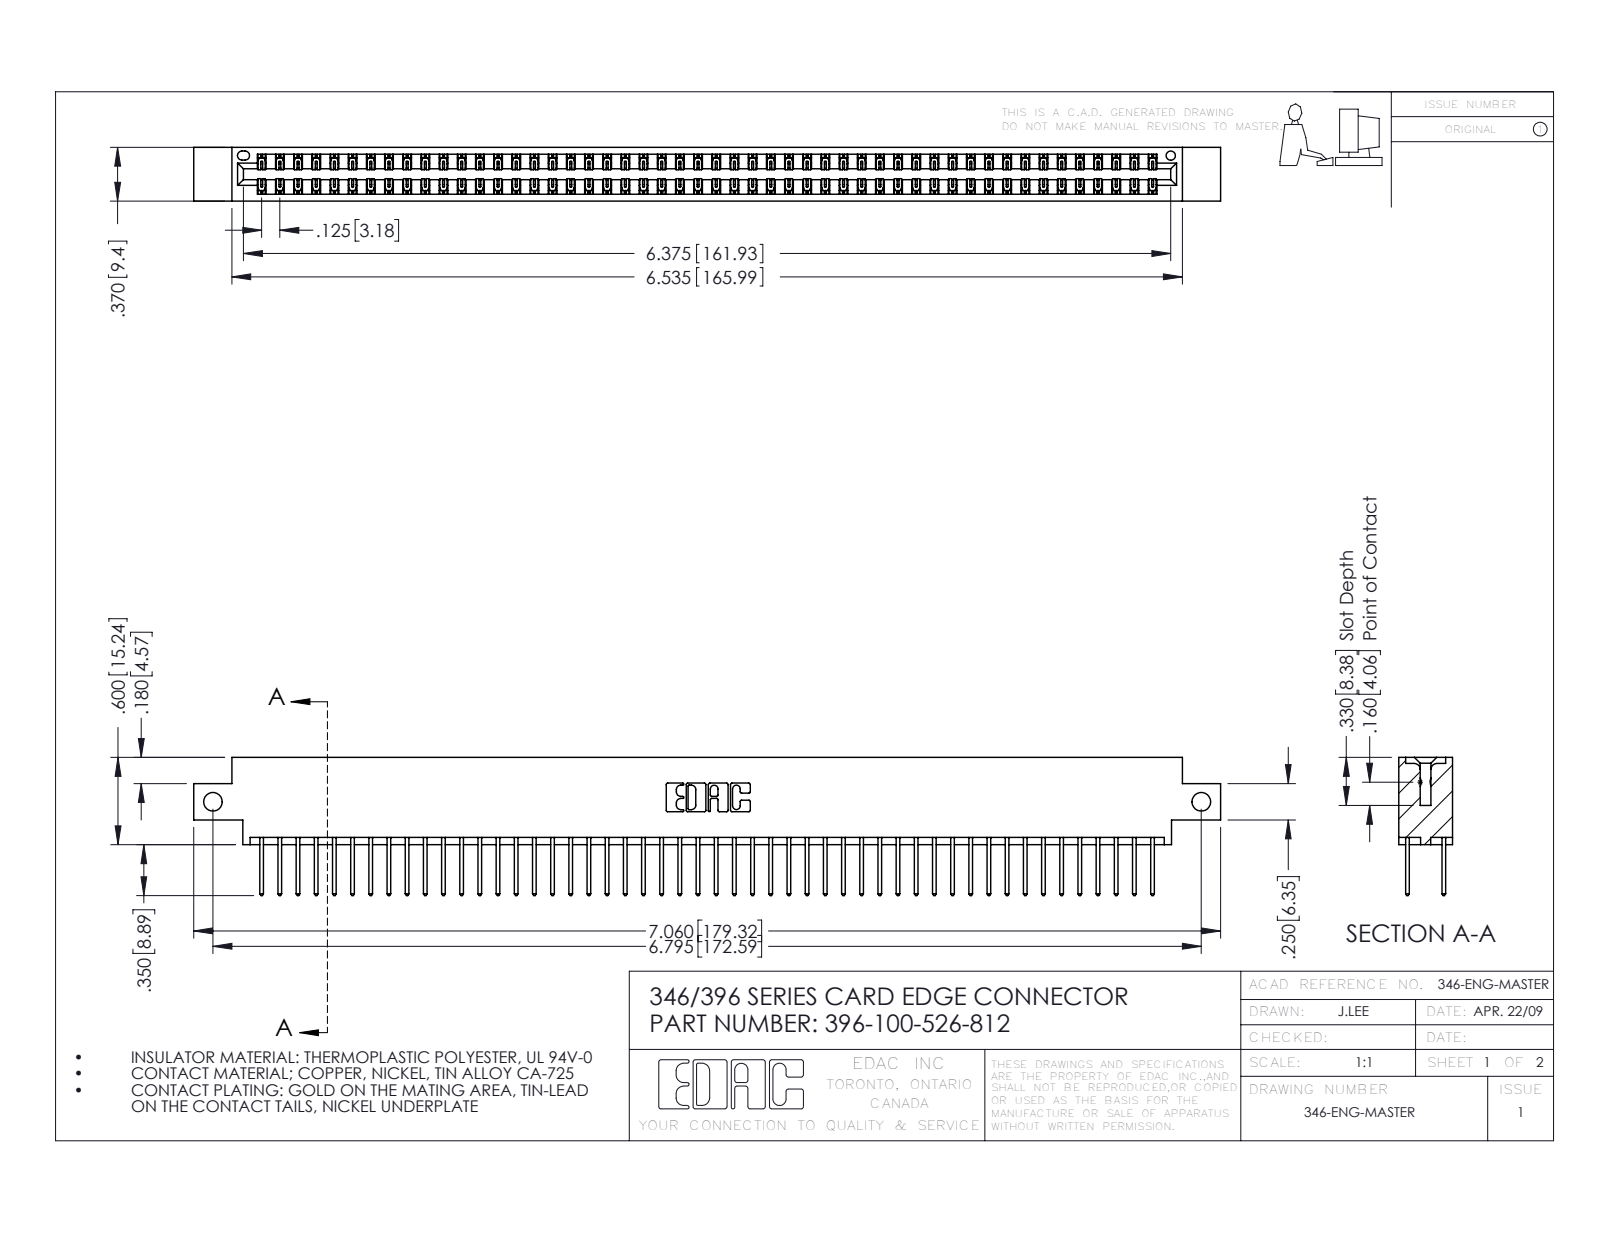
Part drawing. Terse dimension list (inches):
name: 396-100-526-812; 346 Part_0.170 Offset - Side Mount; 345-292-001_345-293-126
written by: SolidWorks 2016 (CONFIG_CONTROL_DESIGN)
unit: in
bodies: 101 solids, 5326 faces (3580 planar, 1746 cylindrical, 0 other)
size: 7.06 × 0.95 × 0.37
volume: 1.066 in³; area: 38.62 in²
holes: 2× ⌀0.128, 1× ⌀0.064
rounds: 150× R0.006, 100× R0.01, 22× R0.01, 6× R0.007, 6× R0.031, 3× R0.026, 2× R0.014, 2× R0.022
face distances: 0.048, 0.322, 0.25, 0.37, 0.072, 0.298, 0.025, 0.275, 0.148, 0.222
hole spacings: 6.795
